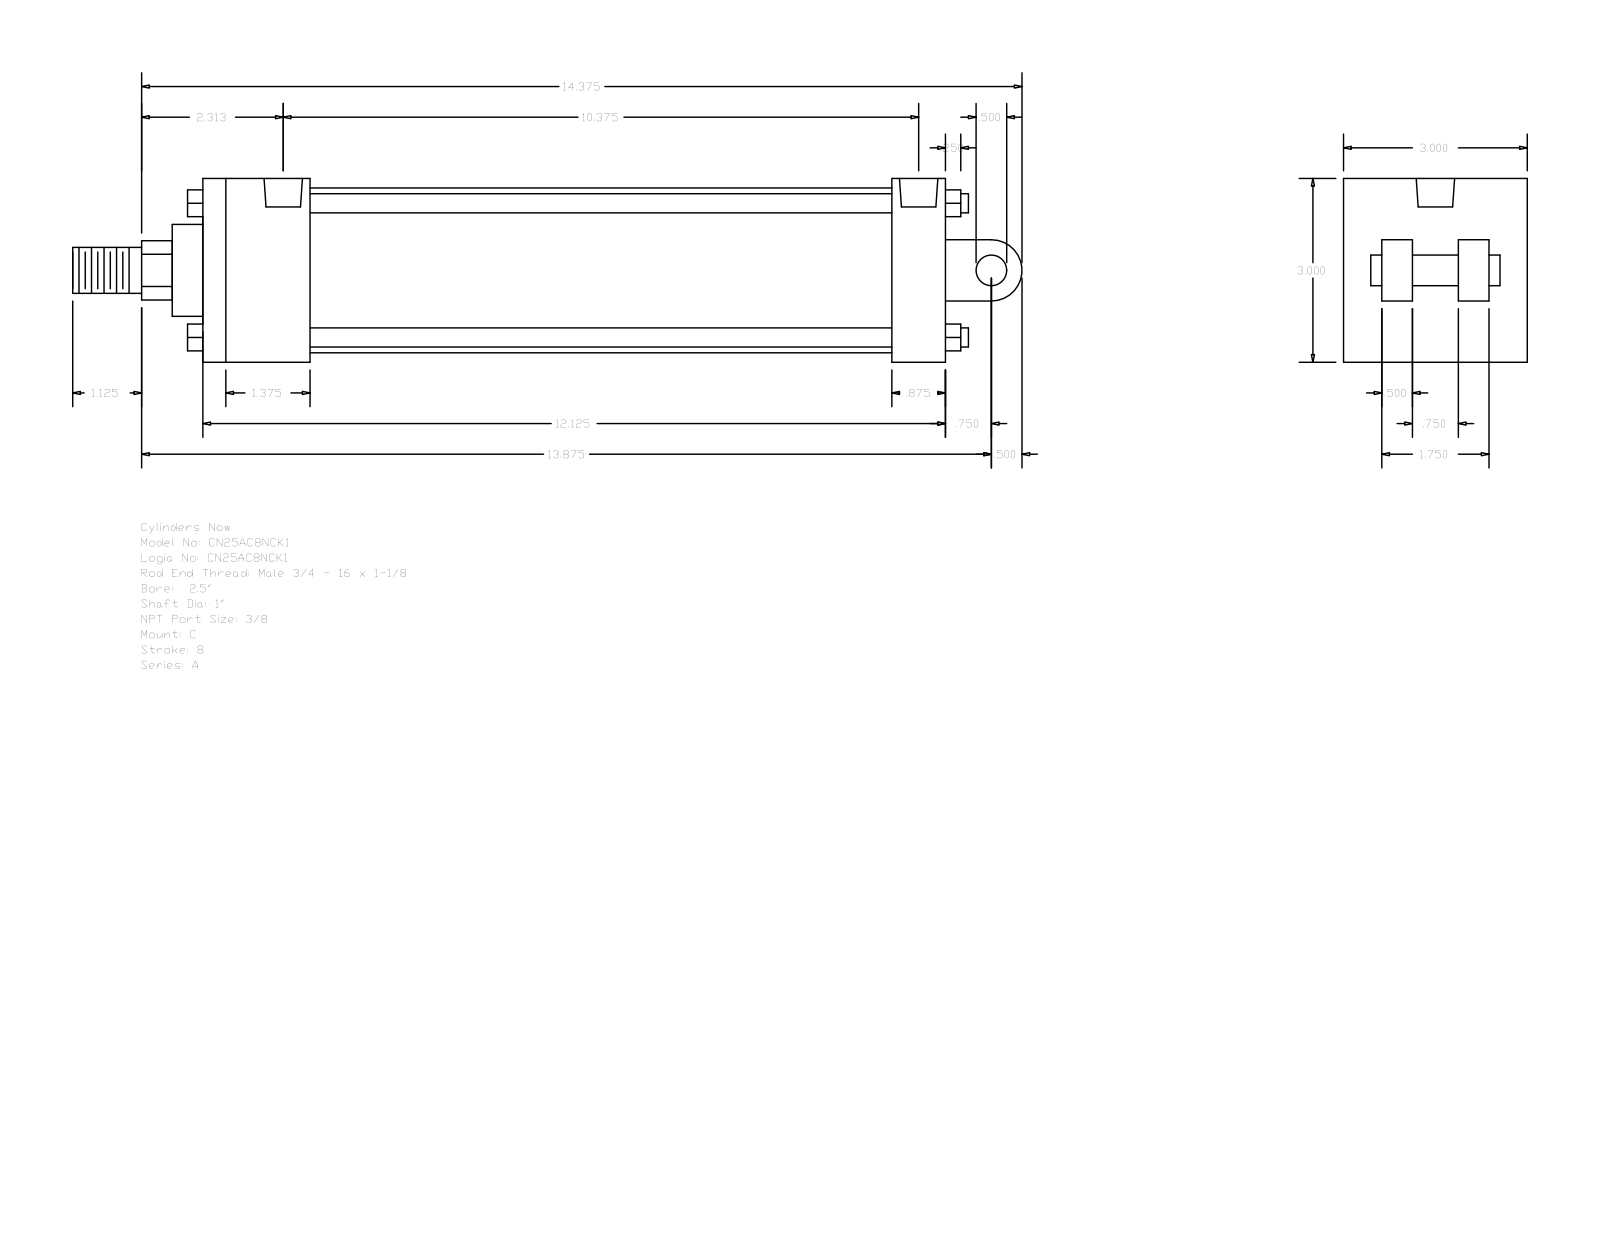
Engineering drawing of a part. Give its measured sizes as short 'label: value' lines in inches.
name: A_C__0250_1
written by: GSSL Pune (CONFIG_CONTROL_DESIGN)
unit: in
bodies: 0 solids, 135 faces (102 planar, 33 cylindrical, 0 other)
size: 15.5 × 3 × 3
holes: 4× ⌀0.219, 2× ⌀0.627
bosses: 4× ⌀0.313, 1× ⌀2.69, 1× ⌀1.5, 1× ⌀1, 1× ⌀0.75, 1× ⌀0.5
rounds: 1× R0.484, 1× R0.5
face distances: 3, 12.125, 0.5, 1.75, 11.25, 9.5, 10.375, 0.875, 0.625, 1
hole spacings: 0.094, 10.469, 10.562, 10.375
